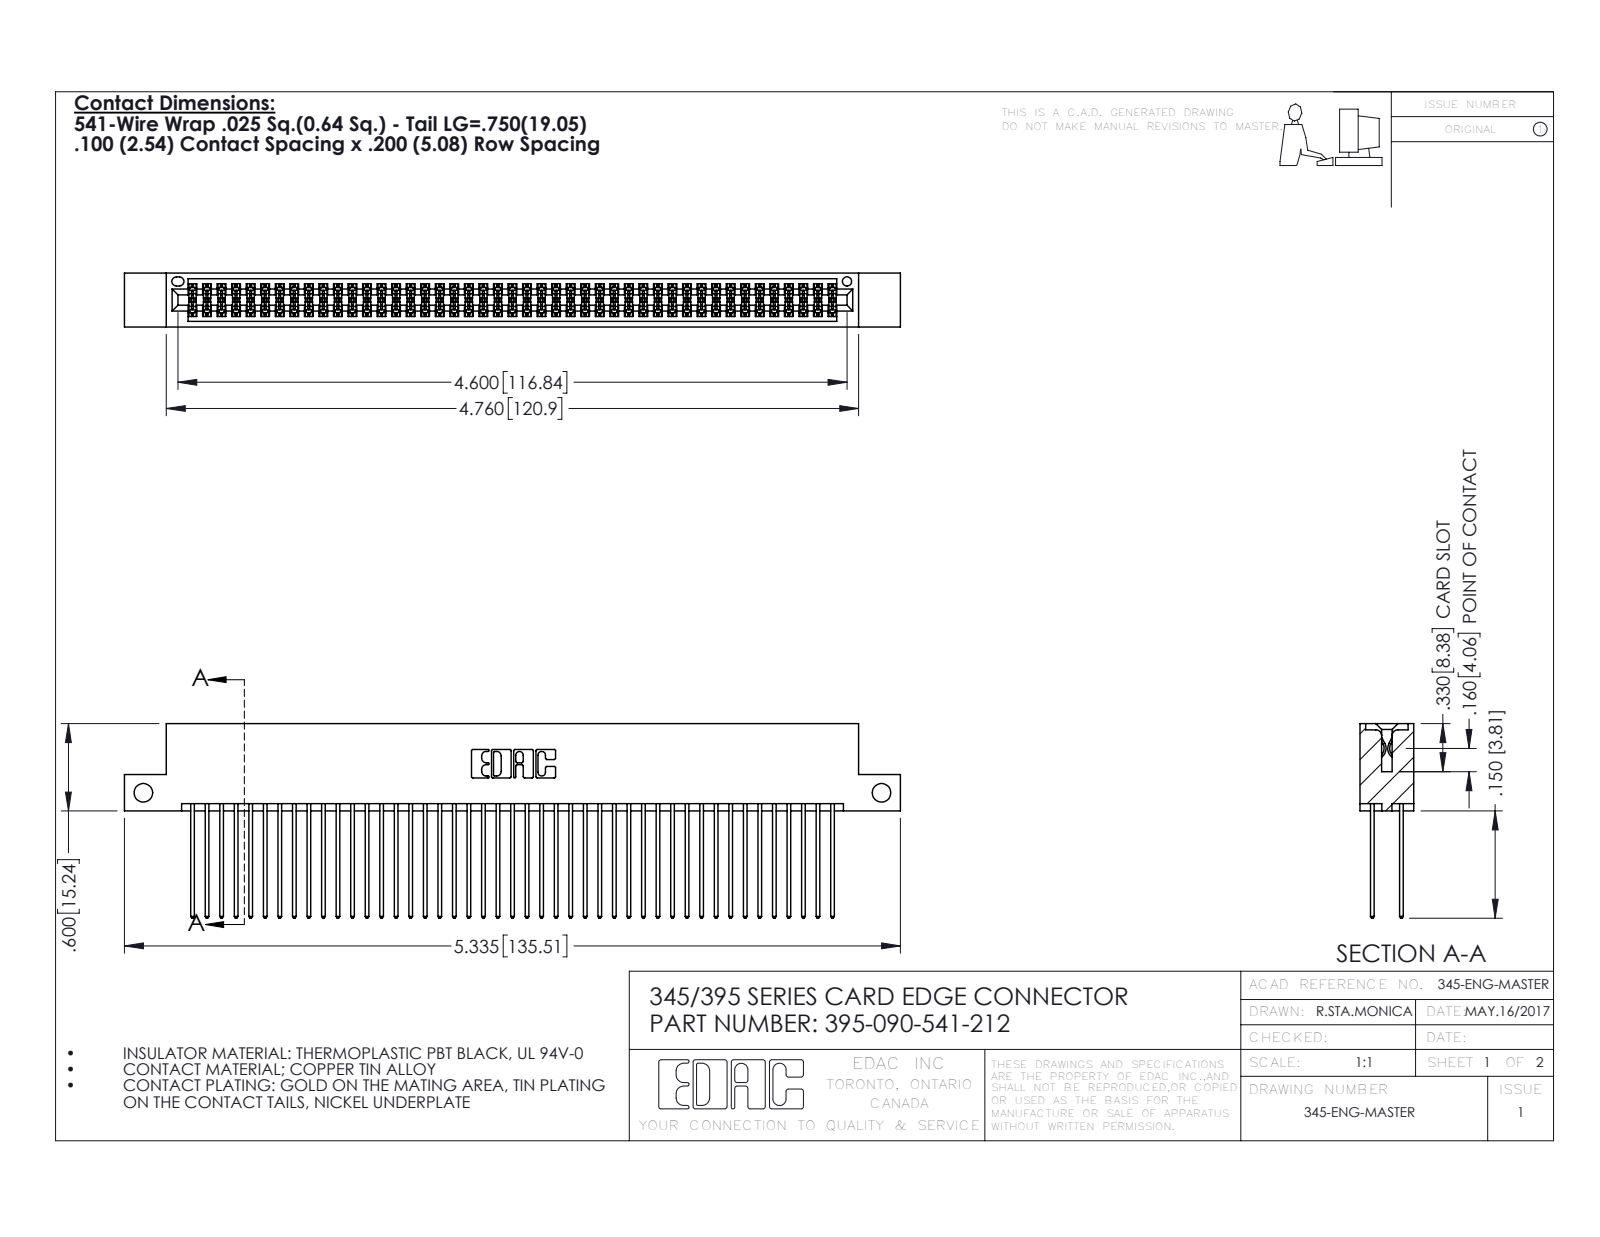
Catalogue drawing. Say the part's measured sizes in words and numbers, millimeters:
The part is named "345 Part_Flush Mounting Lugs - Side Mount; 345-292-001_345-293-141; 395-090-541-212". Its 3-D file was written by "SolidWorks 2016 (CONFIG_CONTROL_DESIGN)". It is 91 solids with 4626 faces: 3050 planar, 1576 cylindrical and 0 other. Overall it measures 135.5 by 34 by 9.4 millimeters. Its volume is 13 600 cubic millimeters and its surface area 22 480 square millimeters. Round holes: 2 of diameter 3.3, 1 of diameter 1.6. Partial cylindrical surfaces (rounded edges, fillets, slot ends): 135 of radius 0.2, 90 of radius 0.3, 22 of radius 0.3, 6 of radius 0.2, 6 of radius 0.8, 3 of radius 0.7, 2 of radius 0.4, 2 of radius 0.5. The main face-to-face distances are 7.6, 1.8, 5.1, 2.5, 6.9, 0.6, 5.7, 9.4, 4.4, 3.8. The hole center spacings are 128.9.
